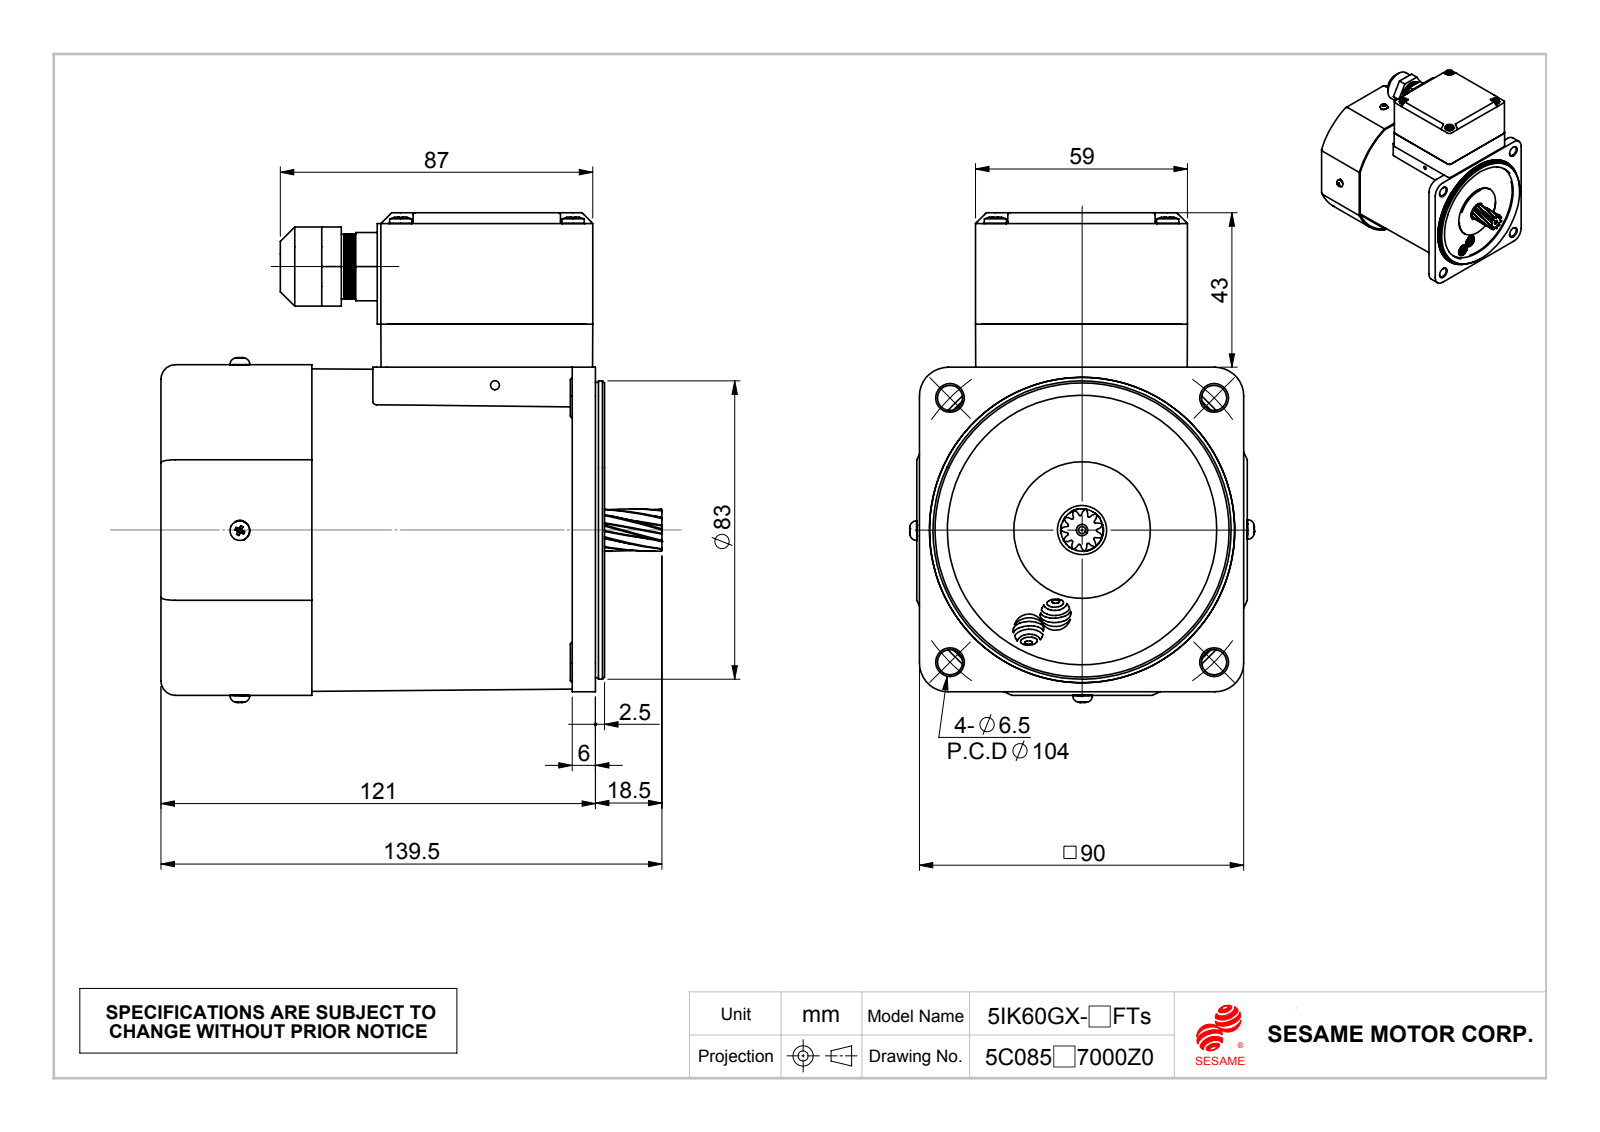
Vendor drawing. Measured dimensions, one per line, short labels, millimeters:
name: 風扇蓋FC-9042-21; 60GX; M560Ts-F; 成品180度 (+1 more)
written by: SolidWorks 2010 (CONFIG_CONTROL_DESIGN)
unit: mm
bodies: 16 solids, 2896 faces (342 planar, 1076 cylindrical, 1478 other)
size: 139.5 × 136.29 × 95.99
volume: 879 224 mm³; area: 138 074 mm²
holes: 5× ⌀2.5, 4× ⌀3.3, 4× ⌀3.5, 4× ⌀3.9, 4× ⌀4.3, 4× ⌀7, 1× ⌀2, 1× ⌀6.5, 1× ⌀11, 1× ⌀12, 1× ⌀13.7, 1× ⌀14.5
bosses: 8× ⌀3, 4× ⌀6.3, 4× ⌀5.5, 1× ⌀85, 1× ⌀84.22, 1× ⌀83, 1× ⌀82.2, 1× ⌀47
rounds: 16× R0.3, 16× R2, 12× R4, 10× R1, 8× R0.5, 8× R0.78, 8× R1.5, 8× R1.66
face distances: 1, 12, 91, 16, 7.3, 118.4, 119.4, 112.1, 111.1, 119.5
hole spacings: 48, 52, 73.54, 11.67, 12.35, 12.7, 24.93, 25
